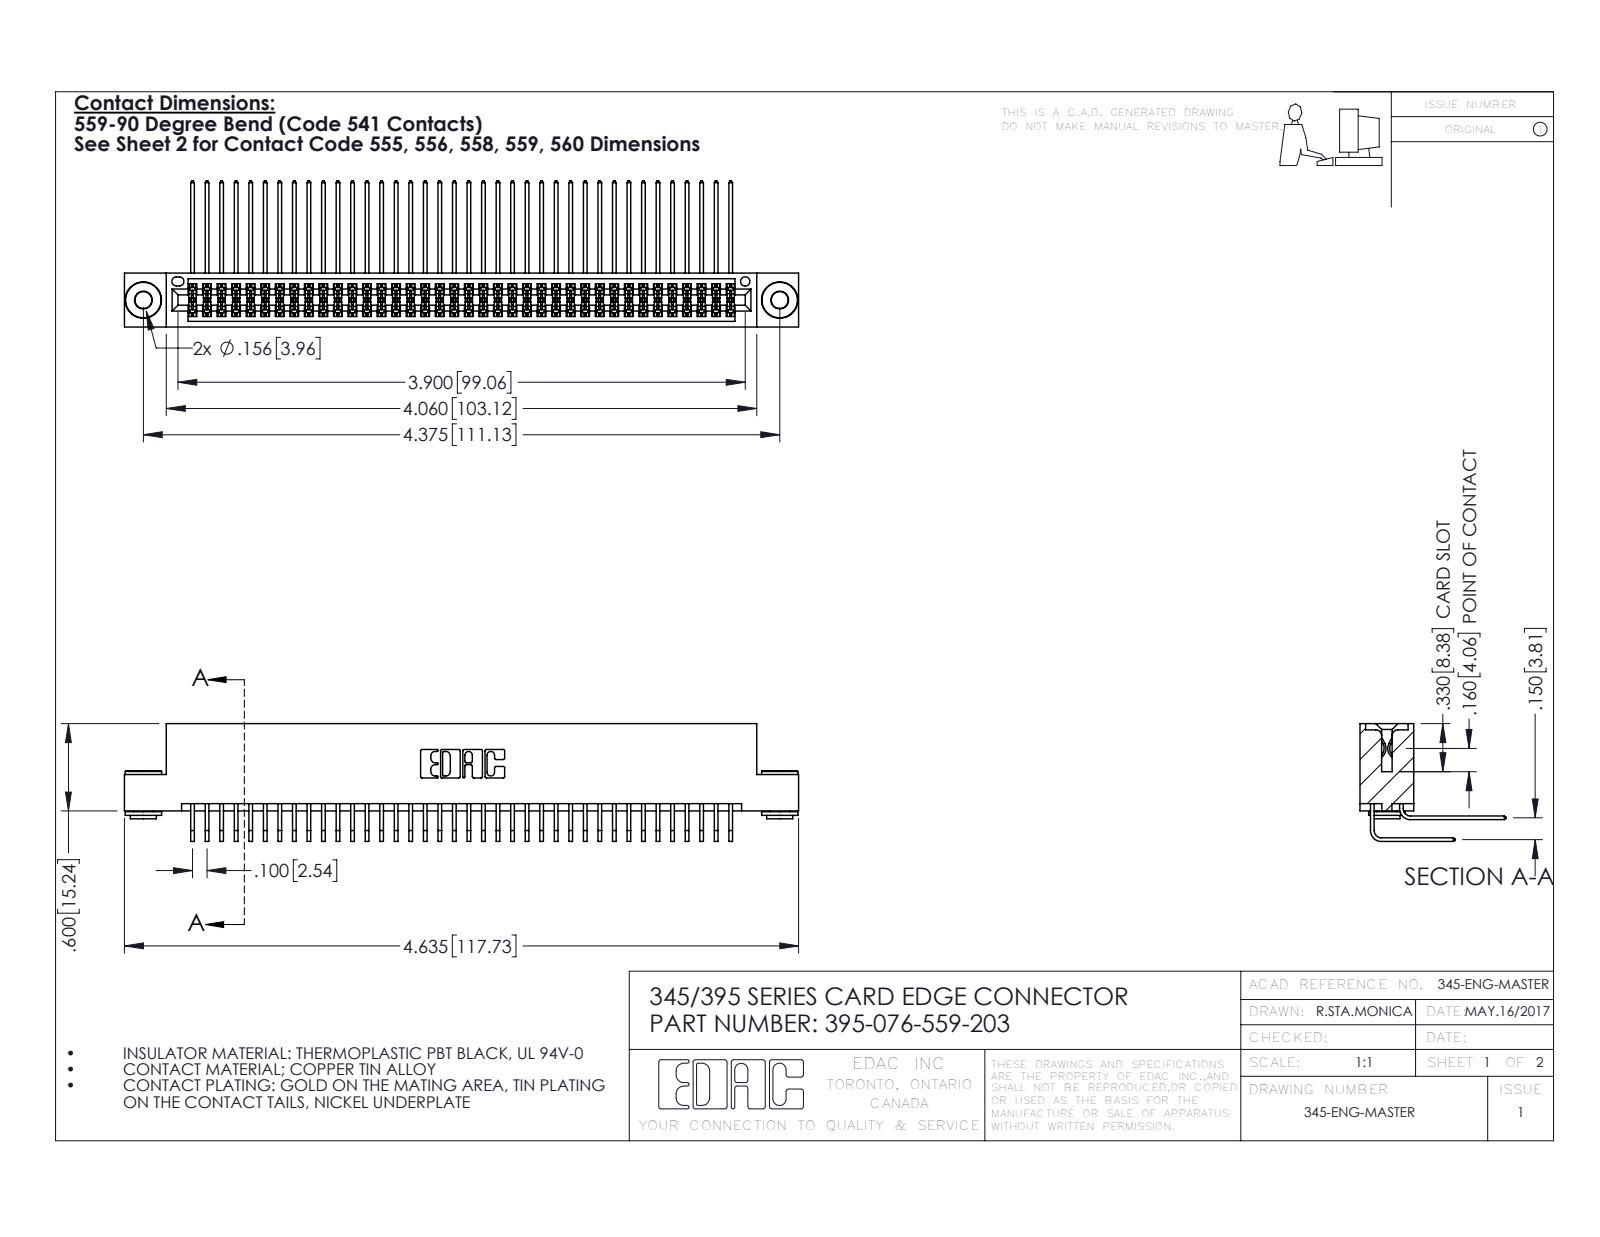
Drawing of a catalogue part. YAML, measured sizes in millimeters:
part_name: "345 Part_Flush Mounting Lugs - 0.156 Dia-TH; 395-076-559-203; 345-292-001_559 Tail - 2; 345-250-002_345-250-002-102 (+1 more)"
step_written_by: "SolidWorks 2016 (CONFIG_CONTROL_DESIGN)"
units: millimeters
bodies: {solids: 79, faces: 4116, planar: 2750, cylindrical: 1358, other: 8}
overall_size: [117.7, 25.5, 20.5]
volume: 11900
surface_area: 19720
round_holes:
  - {diameter: 2.9, count: 2}
  - {diameter: 4, count: 2}
  - {diameter: 1.6, count: 1}
round_bosses_or_shafts:
  - {diameter: 6.4, count: 2}
  - {diameter: 4.6, count: 2}
  - {diameter: 3.5, count: 2}
partial_cylinders:
  - {radius: 0.2, count: 114}
  - {radius: 0.3, count: 22}
  - {radius: 0.2, count: 6}
  - {radius: 0.8, count: 6}
  - {radius: 0.7, count: 3}
  - {radius: 0.4, count: 2}
  - {radius: 0.5, count: 2}
  - {radius: 0.6, count: 2}
face_to_face_distances: [1.8, 7.6, 5.1, 9.4, 0.6, 2.5, 6.9, 5.7, 4.4, 3.8]
hole_center_spacings: [6.9, 105.1, 111.1]
